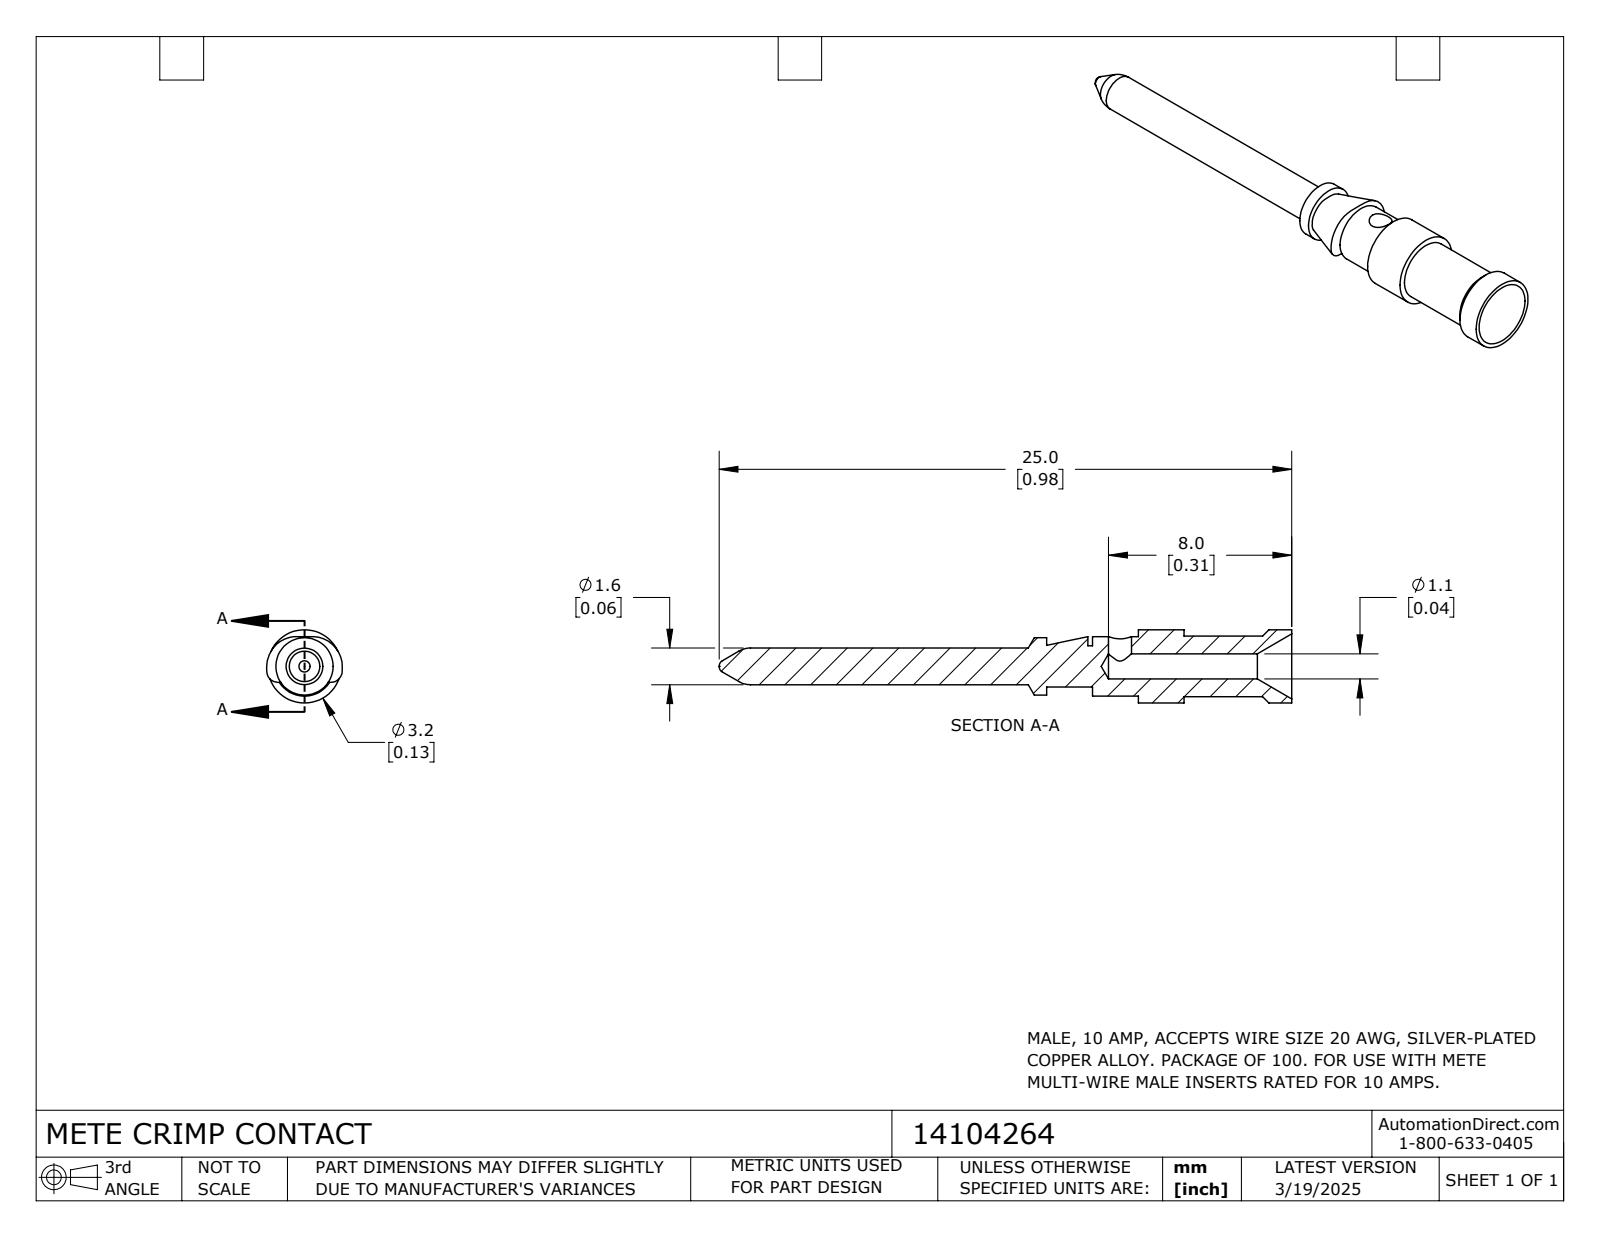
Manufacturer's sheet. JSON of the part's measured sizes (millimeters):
{"part_name": "14104264", "step_written_by": "SolidWorks 2024 (CONFIG_CONTROL_DESIGN)", "units": "millimeters", "bodies": {"solids": 1, "faces": 40, "planar": 7, "cylindrical": 18, "other": 15}, "overall_size": [25, 3.3, 3.2], "volume_mm3": 81, "surface_area_mm2": 218, "round_holes": [[1, 1], [1.1, 1]], "round_bosses_or_shafts": [[3.2, 1], [2.65, 1], [2.6, 1], [2.5, 1], [1.8, 1], [1.6, 1]], "face_to_face_distances": [2, 4, 2.2, 4.2, 6, 1.8, 4.7, 6.7, 8.7, 8.9]}
